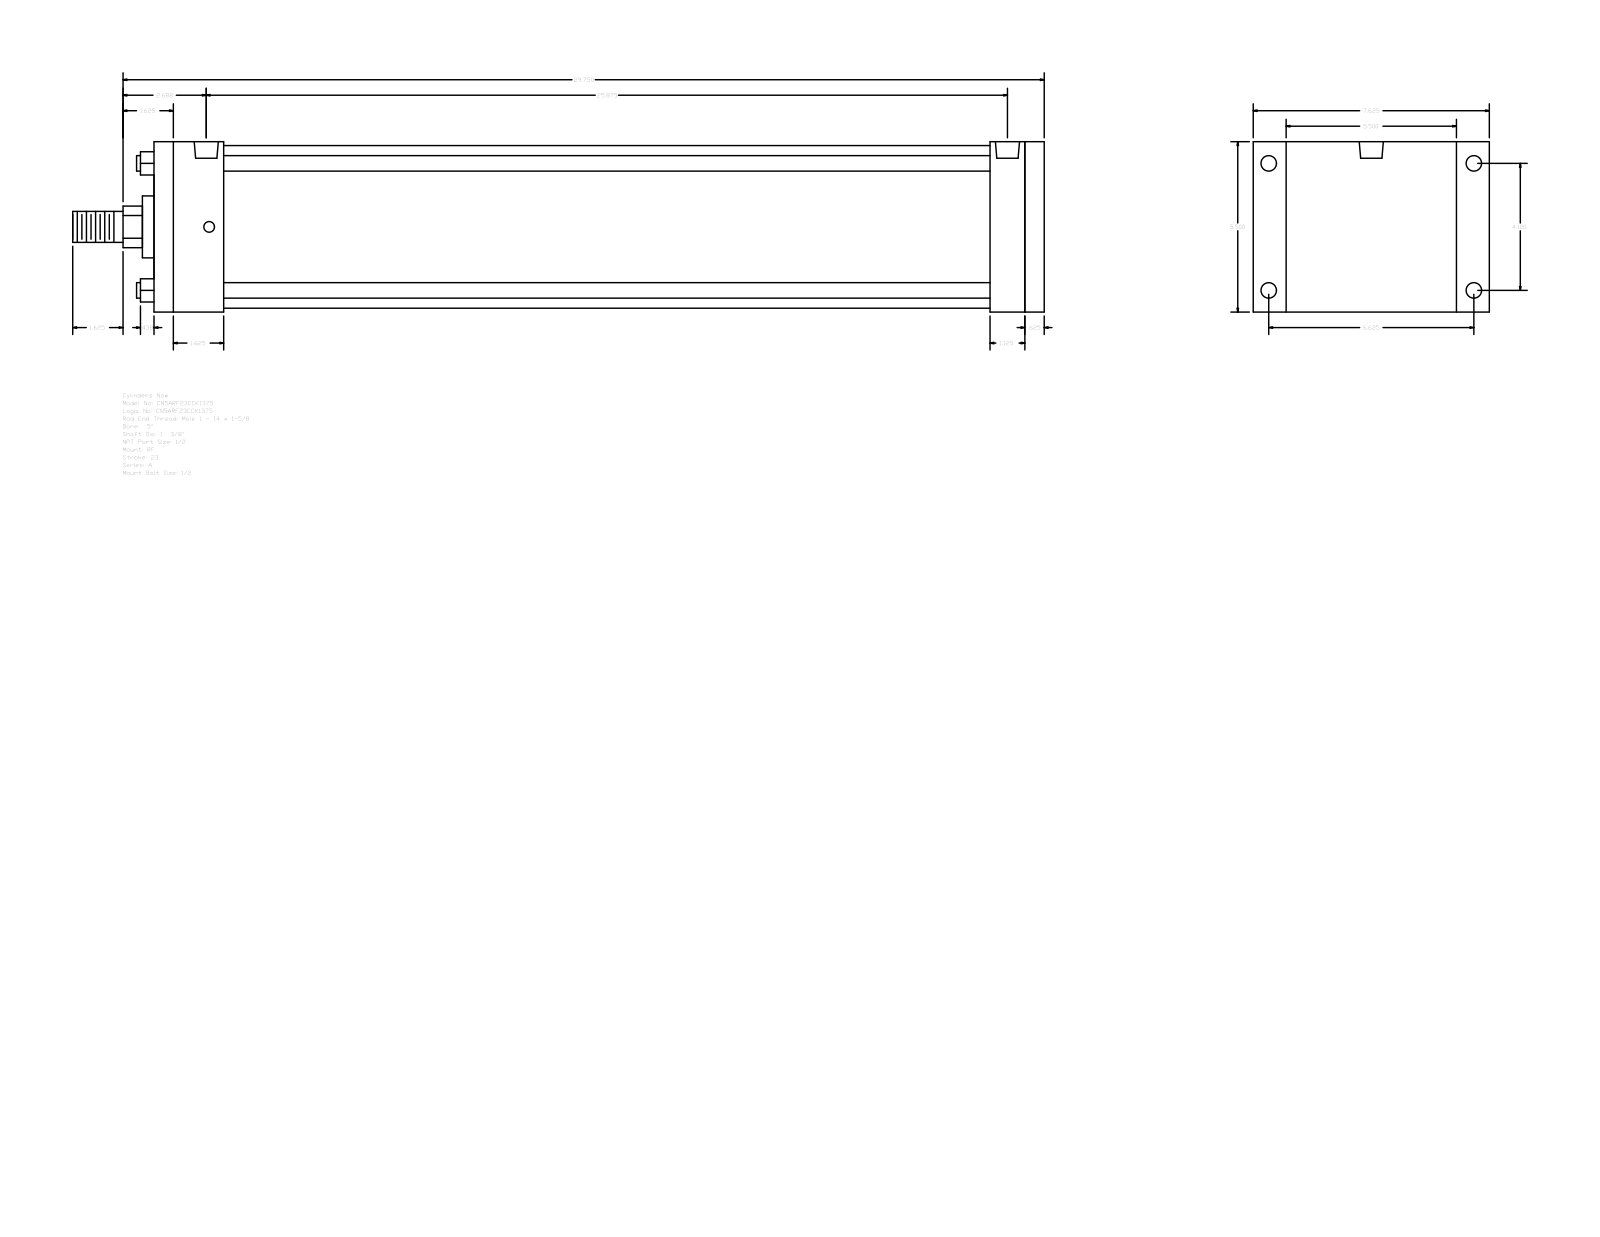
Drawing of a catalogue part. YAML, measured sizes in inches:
part_name: "A_RF__0500_1.375"
step_written_by: "GSSL Pune (CONFIG_CONTROL_DESIGN)"
units: inches
bodies: {solids: 0, faces: 92, planar: 64, cylindrical: 28, other: 0}
overall_size: [31.375, 7.625, 5.5]
round_holes:
  - {diameter: 0.344, count: 4}
  - {diameter: 0.5, count: 4}
  - {diameter: 0.778, count: 2}
round_bosses_or_shafts:
  - {diameter: 0.5, count: 4}
  - {diameter: 5.25, count: 1}
  - {diameter: 2, count: 1}
  - {diameter: 1.375, count: 1}
  - {diameter: 1, count: 1}
partial_cylinders:
  - {radius: 0.672, count: 1}
face_to_face_distances: [5.5, 28.75, 0.625, 28.125, 2.25, 25.875, 26.5, 27, 24.75, 1.125]
hole_center_spacings: [0.094, 4.1, 6.625, 7.791, 25.687, 25.781, 25.875]
